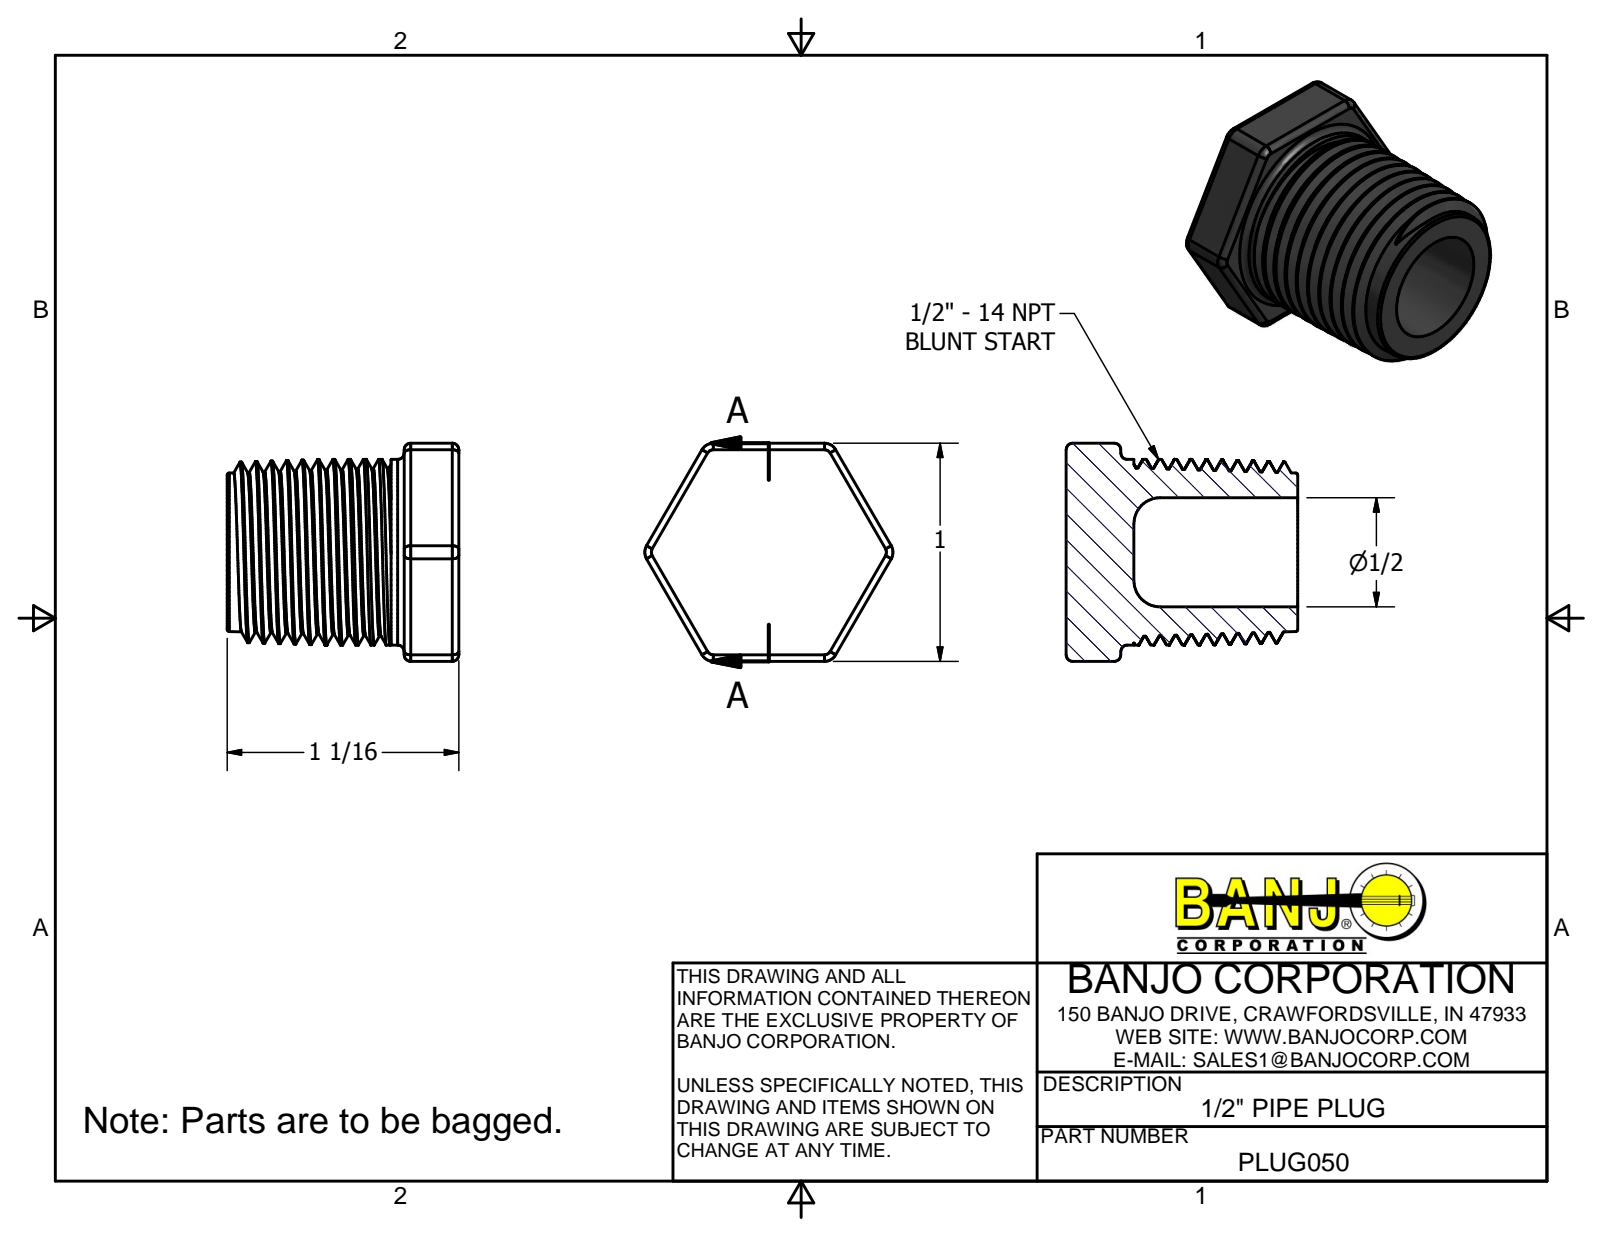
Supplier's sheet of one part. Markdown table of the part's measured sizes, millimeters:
| quantity | value |
| --- | --- |
| part name | PLUG050U |
| STEP written by | Autodesk Inventor 2017 (AUTOMOTIVE_DESIGN) |
| units | millimeters |
| bodies | 1 solid, 67 faces (11 planar, 25 cylindrical, 31 other) |
| overall size | 28.86 × 26.92 × 25.4 |
| volume | 7 827 mm³ |
| surface area | 4 371 mm² |
| round holes (diameter × count) | 12.7 × 1 |
| round bosses / shafts (diameter × count) | 21.62 × 1 |
| partial cylindrical surfaces (radius × count) | 0.76 × 12, 1.52 × 6, 5.88 × 1 |
| main face-to-face distances | 25.4, 26.93, 6.35, 20.58, 7.88, 1.53, 19.05 |
